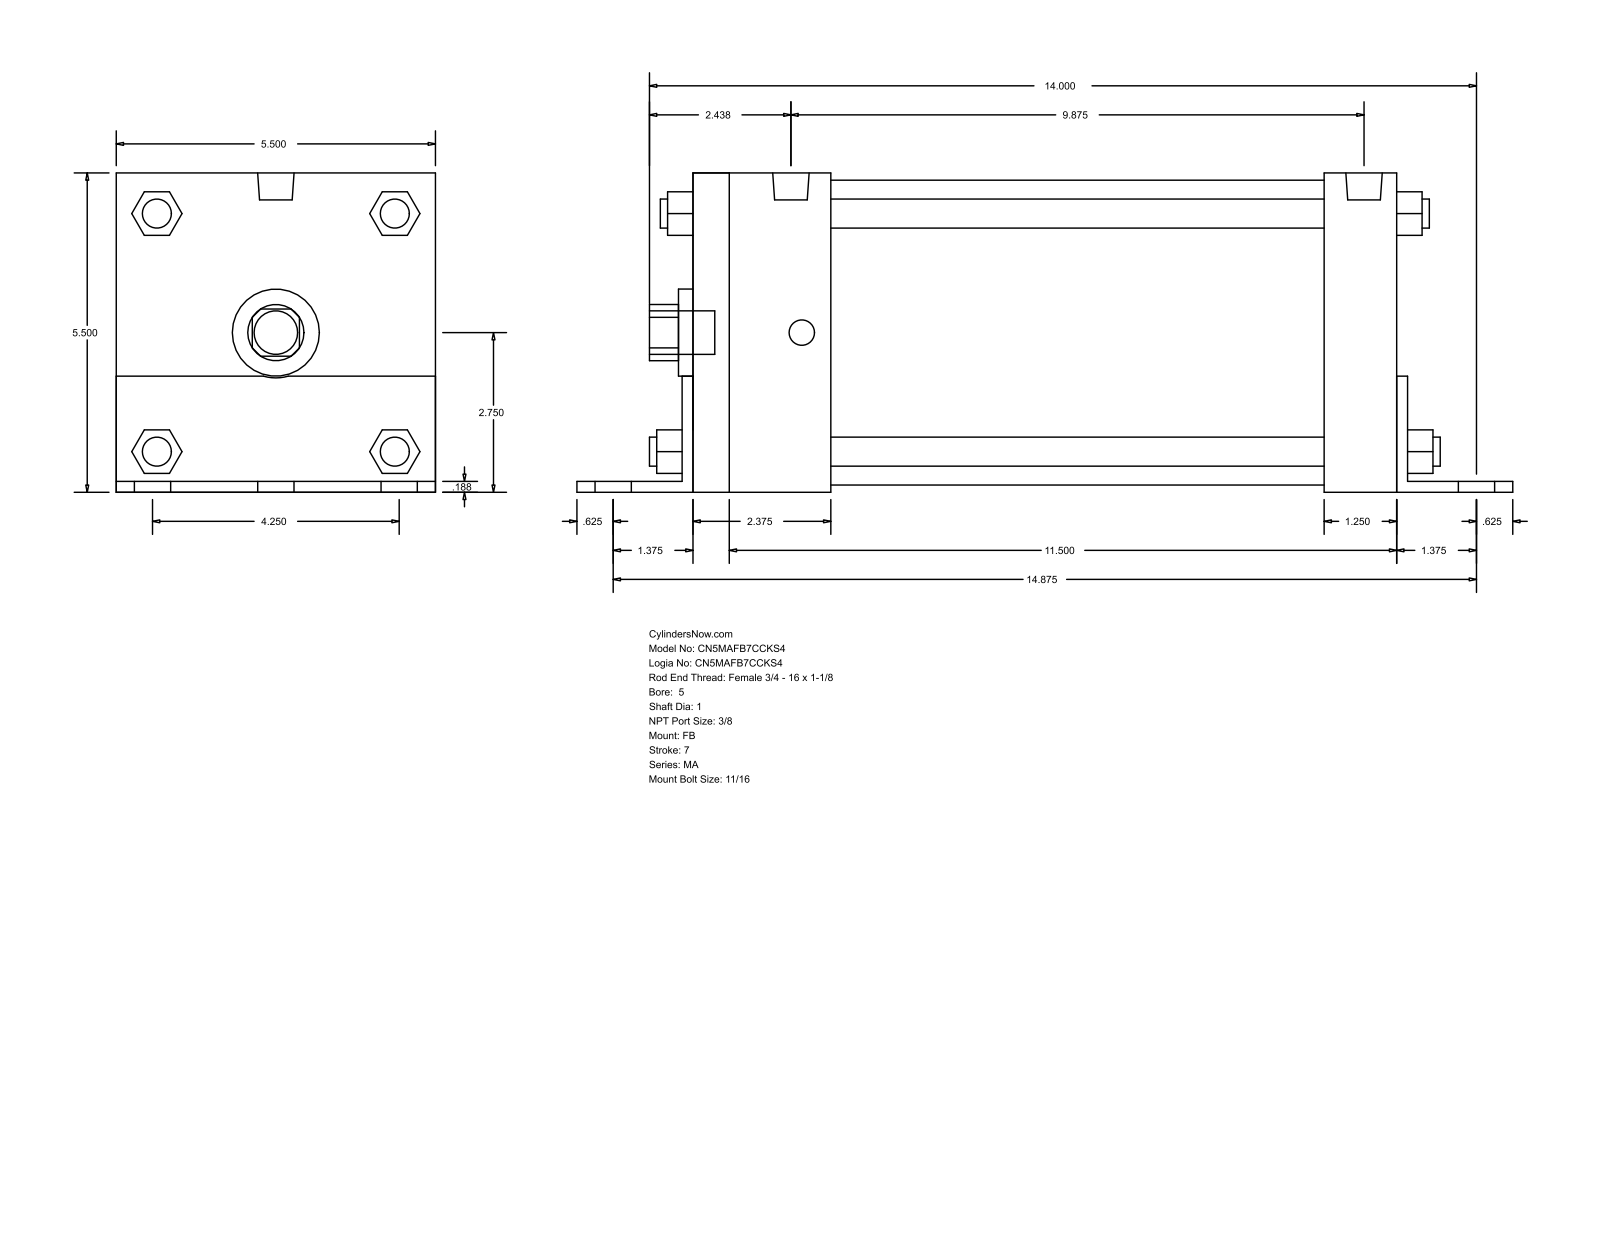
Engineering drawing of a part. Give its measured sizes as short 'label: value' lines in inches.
name: MA_FB__0500_1
written by: GSSL Pune (CONFIG_CONTROL_DESIGN)
unit: in
bodies: 0 solids, 140 faces (105 planar, 35 cylindrical, 0 other)
size: 16.125 × 5.502 × 5.5
holes: 1× ⌀1, 1× ⌀1.5, 1× ⌀5.25
bosses: 6× ⌀0.687, 4× ⌀0.5, 4× ⌀0.437, 2× ⌀0.627, 1× ⌀0.75
rounds: 1× R0.484, 1× R0.78
face distances: 5.5, 0.187, 5.502, 0.185, 5.315, 12.125, 0.188, 12.313, 12.5, 12.312
